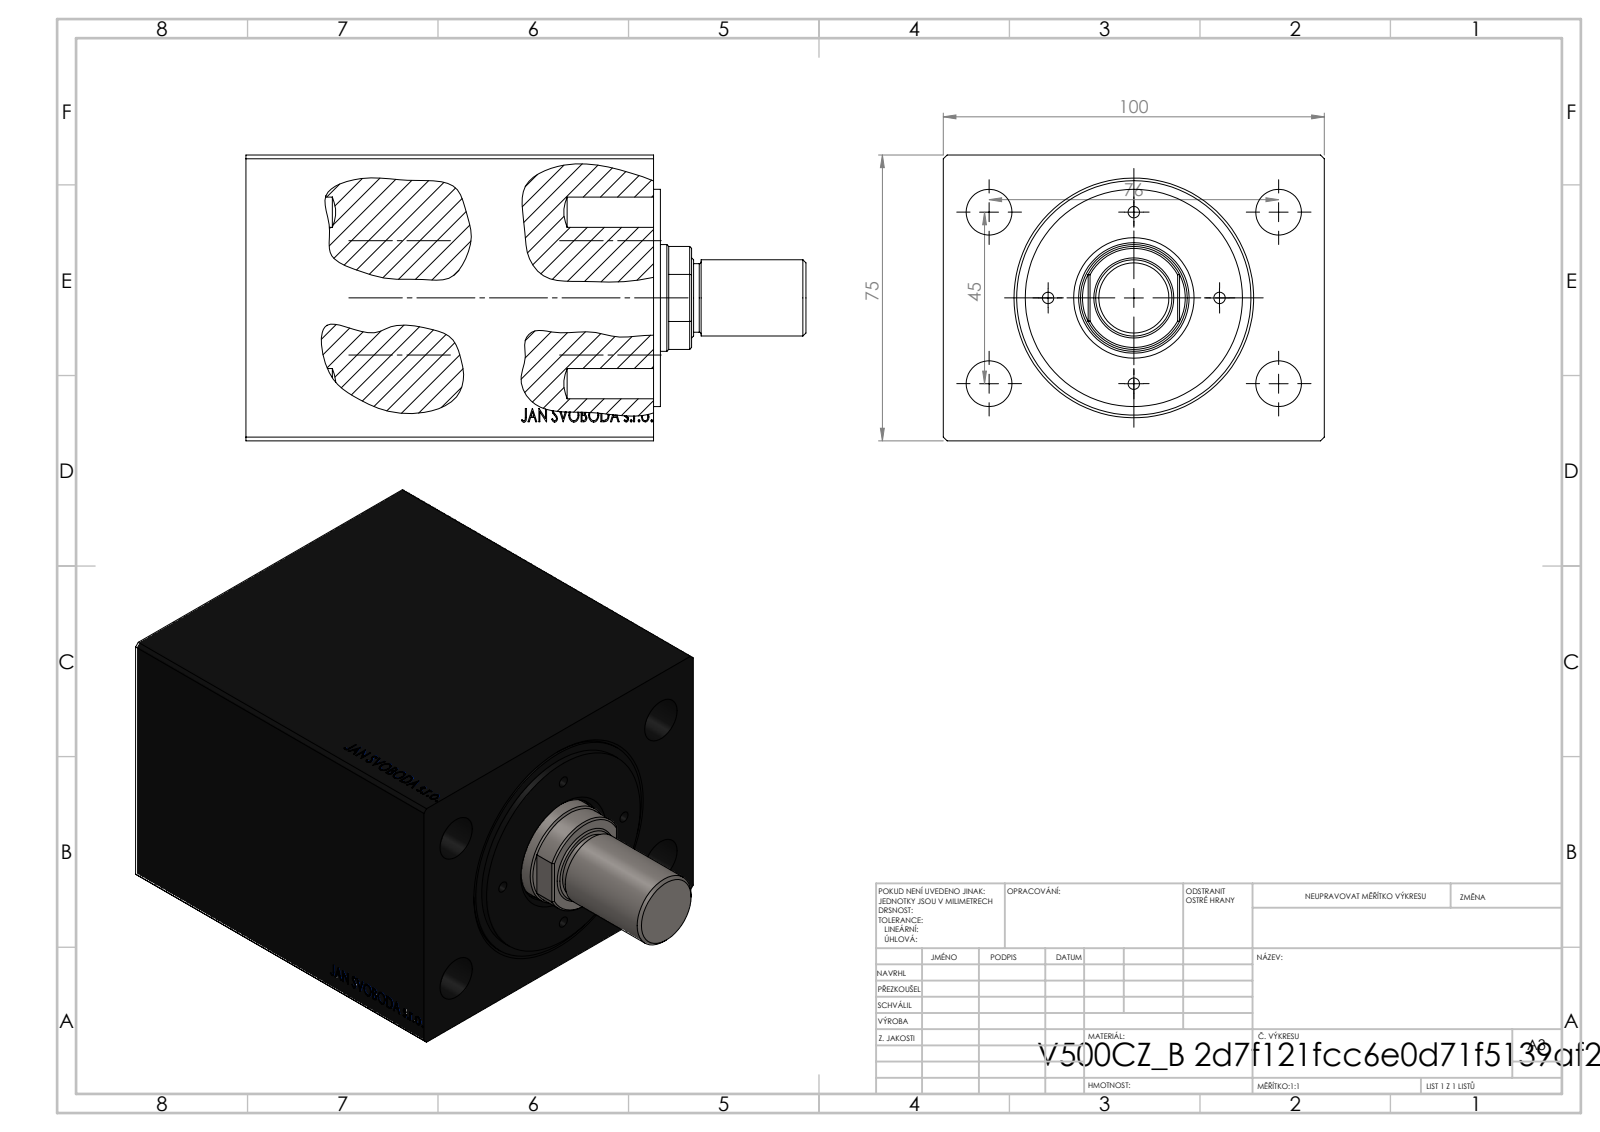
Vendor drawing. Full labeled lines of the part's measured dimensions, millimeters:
Part name (STEP PRODUCT): V500CZ_MALE_METRIC; V500CZ_B_VC; V500CZ
STEP written by: SolidWorks 2019 (CONFIG_CONTROL_DESIGN)
Units: millimetres
Bodies: 4 solids, 887 faces (403 planar, 62 cylindrical, 422 other)
Overall size (bounding box): 147 × 100 × 75
Volume: 820 428 mm³ · Surface area: 125 556 mm²
Round holes (diameter × count): ⌀3 ×4, ⌀12 ×4, ⌀5.5 ×2, ⌀13.16 ×2, ⌀20 ×2, ⌀18.5 ×1, ⌀28 ×1, ⌀29 ×1, ⌀36 ×1, ⌀50 ×1, ⌀61.5 ×1
Round bosses / shafts (diameter × count): ⌀57 ×1, ⌀20 ×1, ⌀18 ×1
Partial cylindrical surfaces — rounded edges, fillets, slot ends (radius × count): R13.5 ×1
Main face-to-face distances: 75, 100, 107, 89.5, 17.5, 82, 7.5, 25, 91.3, 1.8
Hole centre spacings: 22.5, 27.32, 31.82, 38, 44.16, 45, 58.9, 64.55
